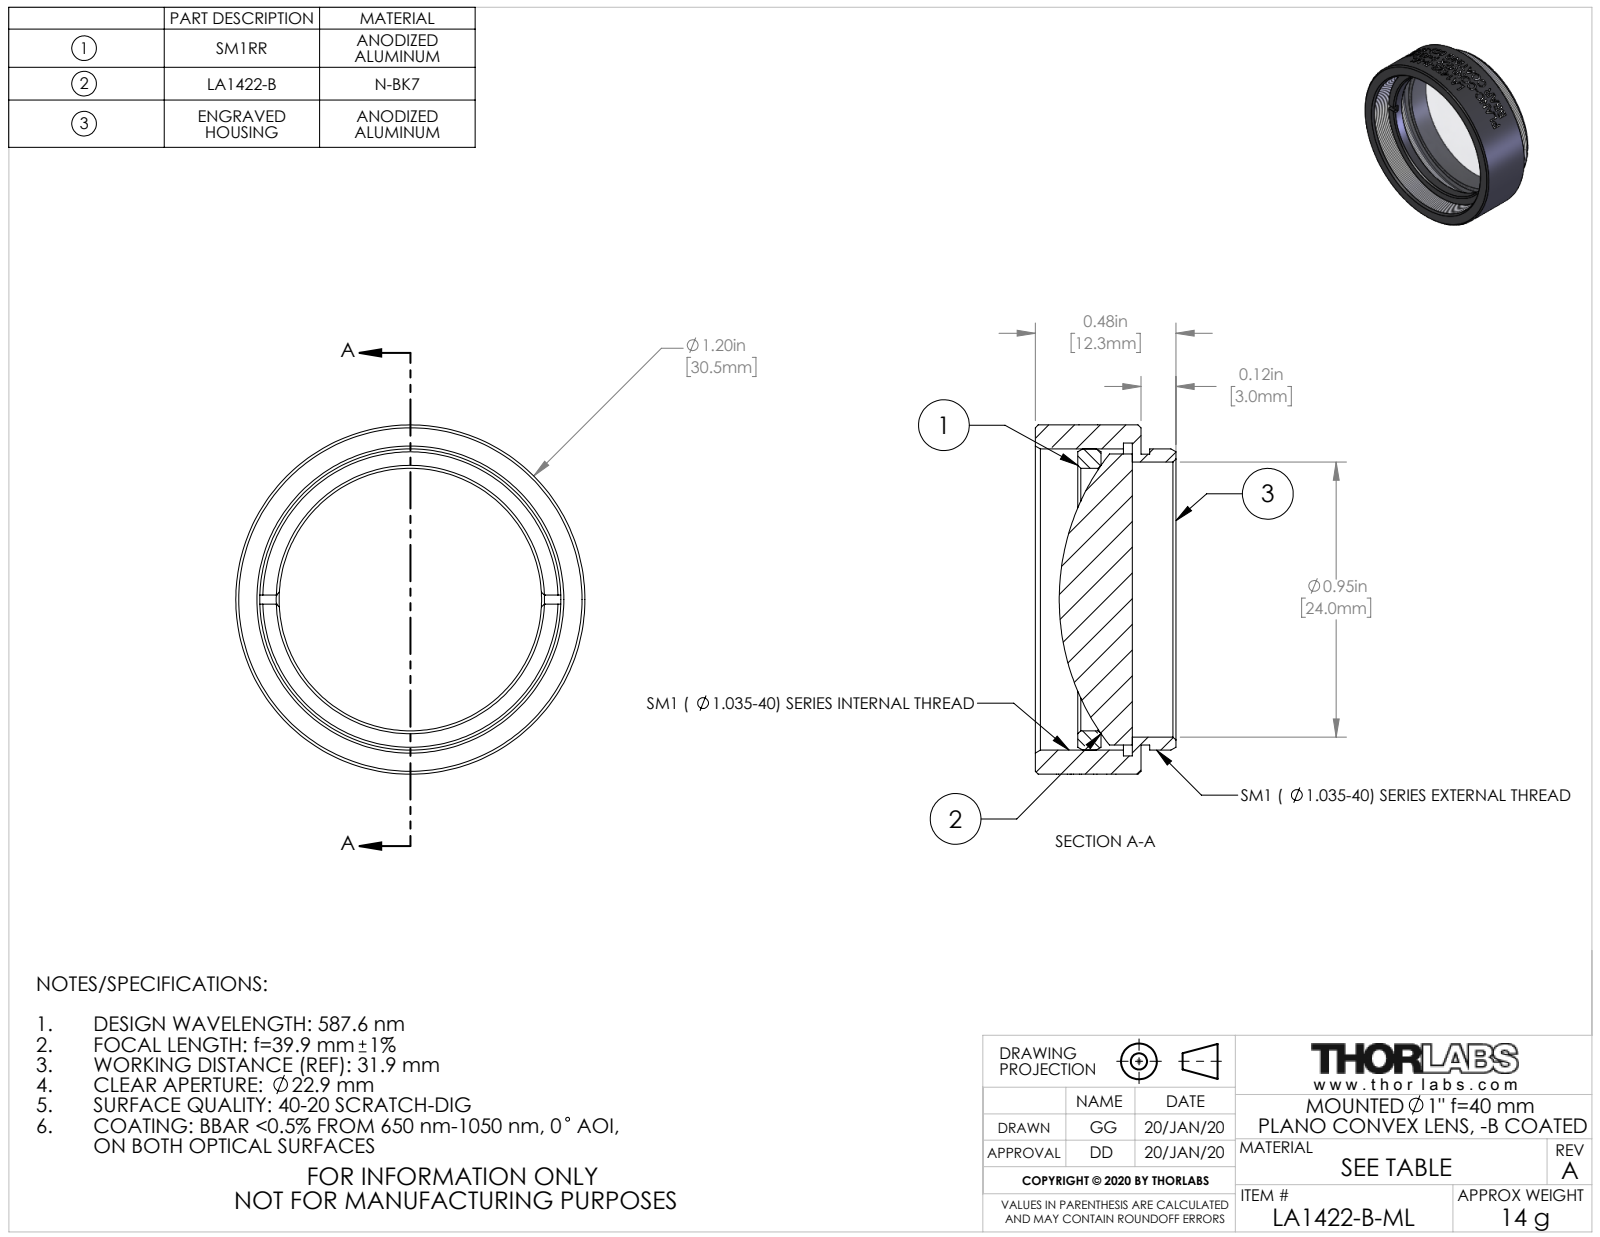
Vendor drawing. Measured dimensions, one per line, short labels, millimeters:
name: TTN203739-E0W
written by: SolidWorks 2018 (CONFIG_CONTROL_DESIGN)
unit: mm
bodies: 3 solids, 157 faces (20 planar, 113 cylindrical, 24 other)
size: 30.48 × 30.48 × 12.27
volume: 4 399 mm³; area: 4 521 mm²
holes: 1× ⌀22.91, 1× ⌀24, 1× ⌀27.3
bosses: 1× ⌀30.48, 1× ⌀26.29, 1× ⌀25.4, 1× ⌀25.37
face distances: 0.77, 9.22, 8.45, 3.48, 2.71, 5.74, 5.52, 4.75, 2.04, 3.7
